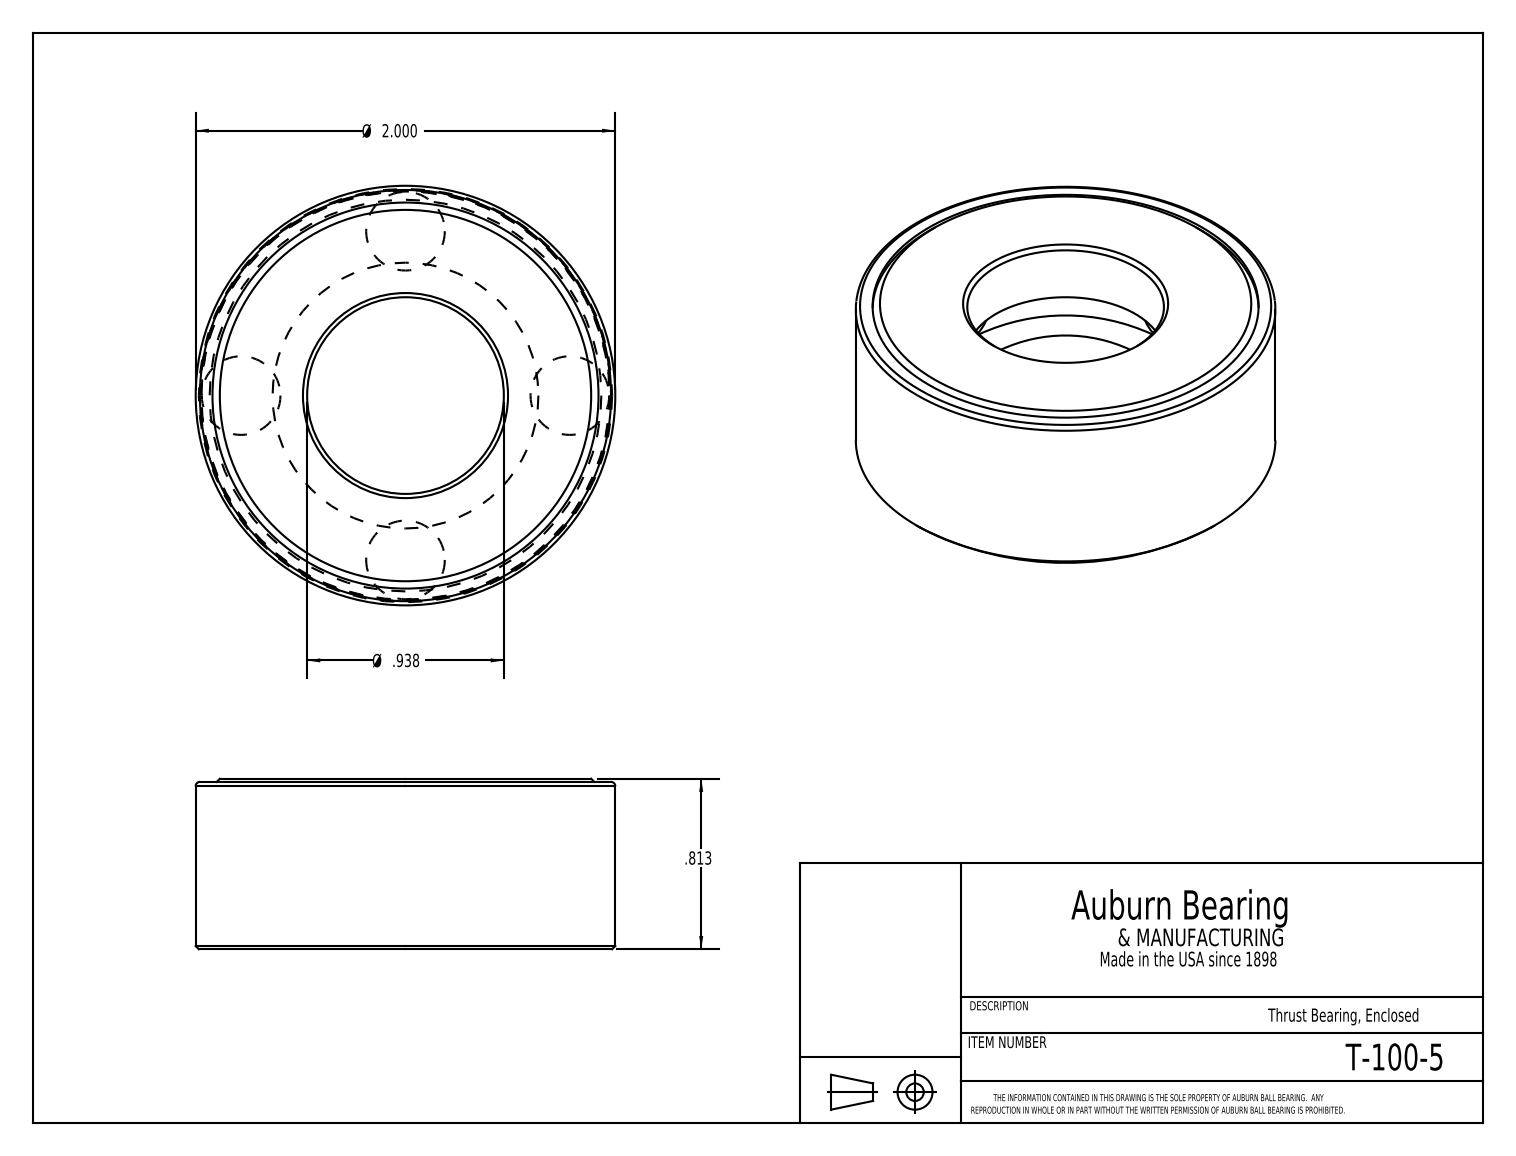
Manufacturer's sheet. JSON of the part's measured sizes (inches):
{"part_name": "T-100-5", "step_written_by": "SolidWorks 2016 (CONFIG_CONTROL_DESIGN)", "units": "inches", "bodies": {"solids": 6, "faces": 28, "planar": 9, "cylindrical": 7, "other": 12}, "overall_size": [2, 2, 0.813], "volume_in3": 1.391, "surface_area_in2": 23.6, "round_holes": [[0.937, 1], [1.84, 1], [1.96, 1]], "round_bosses_or_shafts": [[2, 1], [1.946, 1]], "face_to_face_distances": [0.813, 0.294, 0.519, 0.225, 0.778, 0.484, 0.259, 0.035, 0.798, 0.504]}
